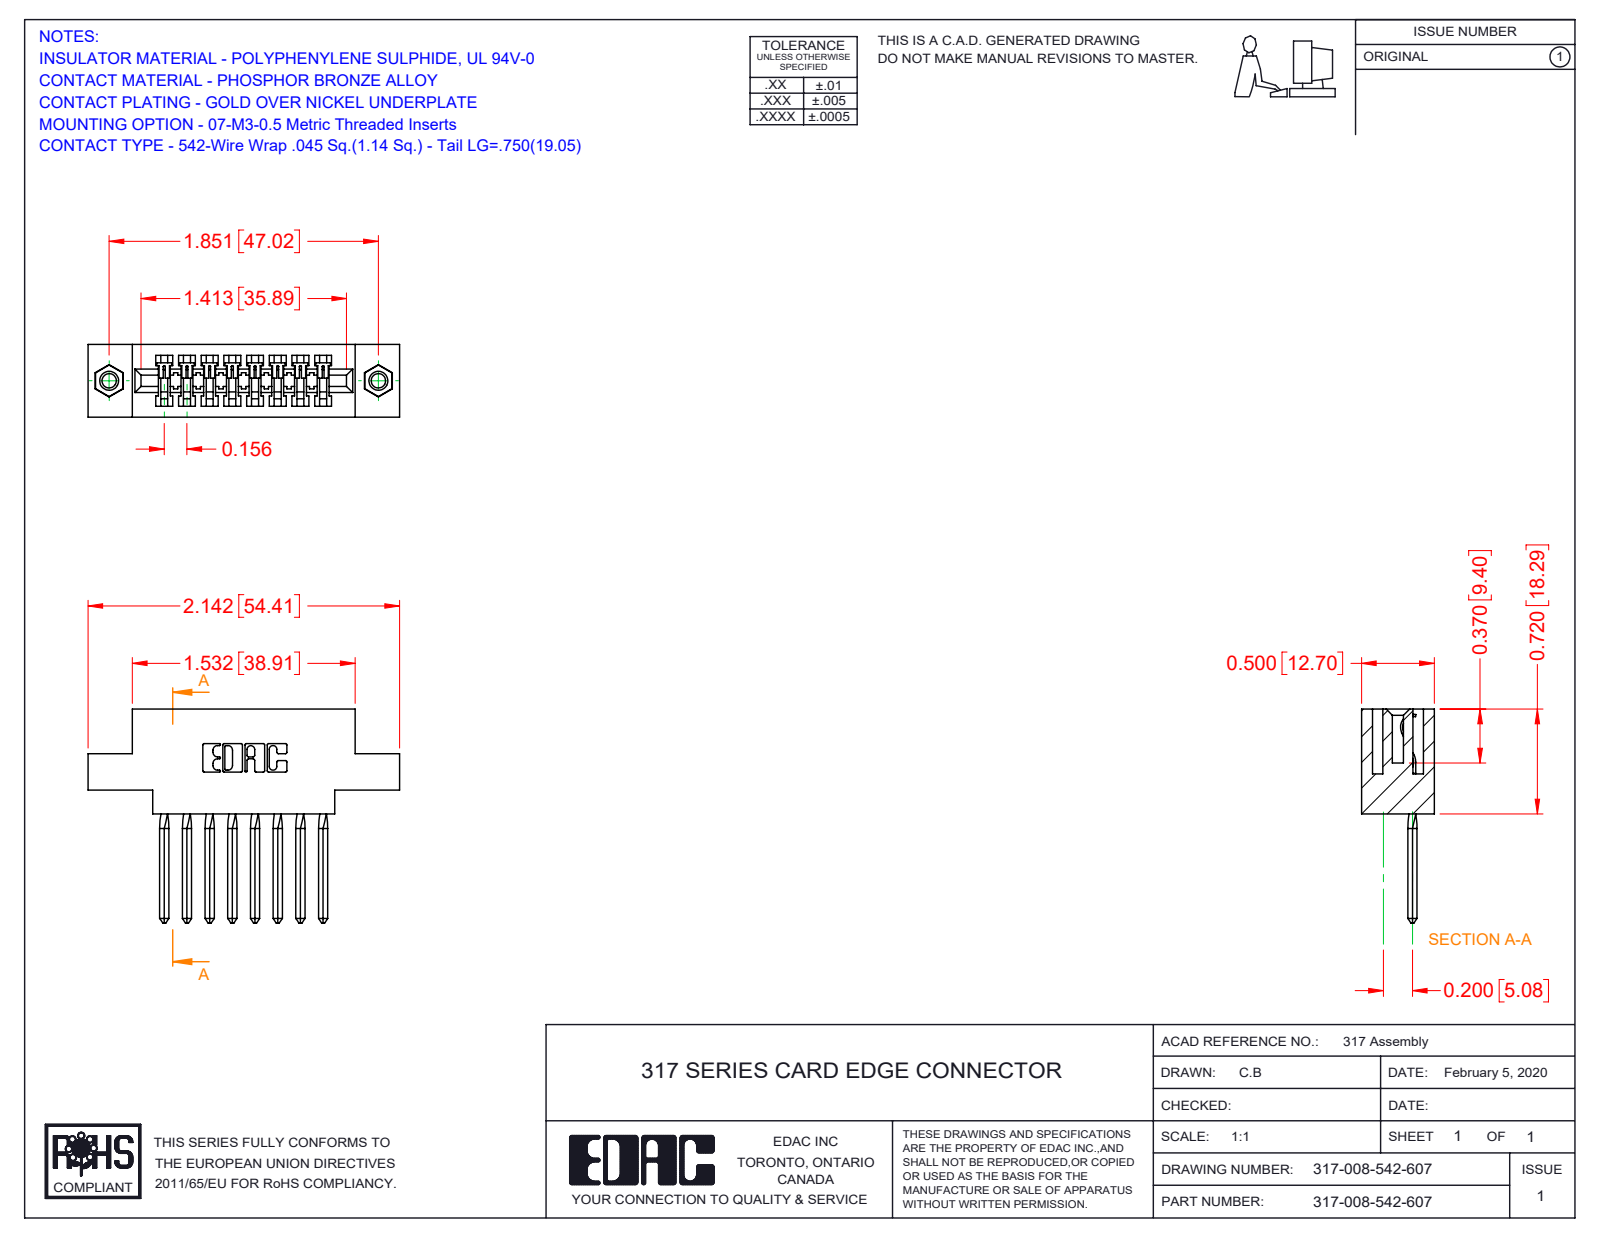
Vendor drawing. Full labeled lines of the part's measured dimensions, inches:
Part name (STEP PRODUCT): 317-008-542-607; 345-250-001_345-250-005-103; 317-290-003_542; 317 Part_.156 Dia - TI
STEP written by: SolidWorks 2016 (CONFIG_CONTROL_DESIGN)
Units: inches
Bodies: 11 solids, 762 faces (602 planar, 112 cylindrical, 48 other)
Overall size (bounding box): 2.142 × 1.47 × 0.5
Volume: 0.457 in³ · Surface area: 13.03 in²
Round holes (diameter × count): ⌀0.098 ×2, ⌀0.125 ×2, ⌀0.156 ×2
Round bosses / shafts (diameter × count): ⌀0.155 ×2
Partial cylindrical surfaces — rounded edges, fillets, slot ends (radius × count): R0.01 ×22, R0.006 ×16, R0.007 ×6, R0.031 ×6, R0.026 ×3, R0.074 ×1, R0.089 ×1, R0.1 ×1
Main face-to-face distances: 0.5, 0.075, 0.425, 0.11, 0.065, 0.22, 0.156, 0.116, 0.136, 0.35
Hole centre spacings: 1.851
